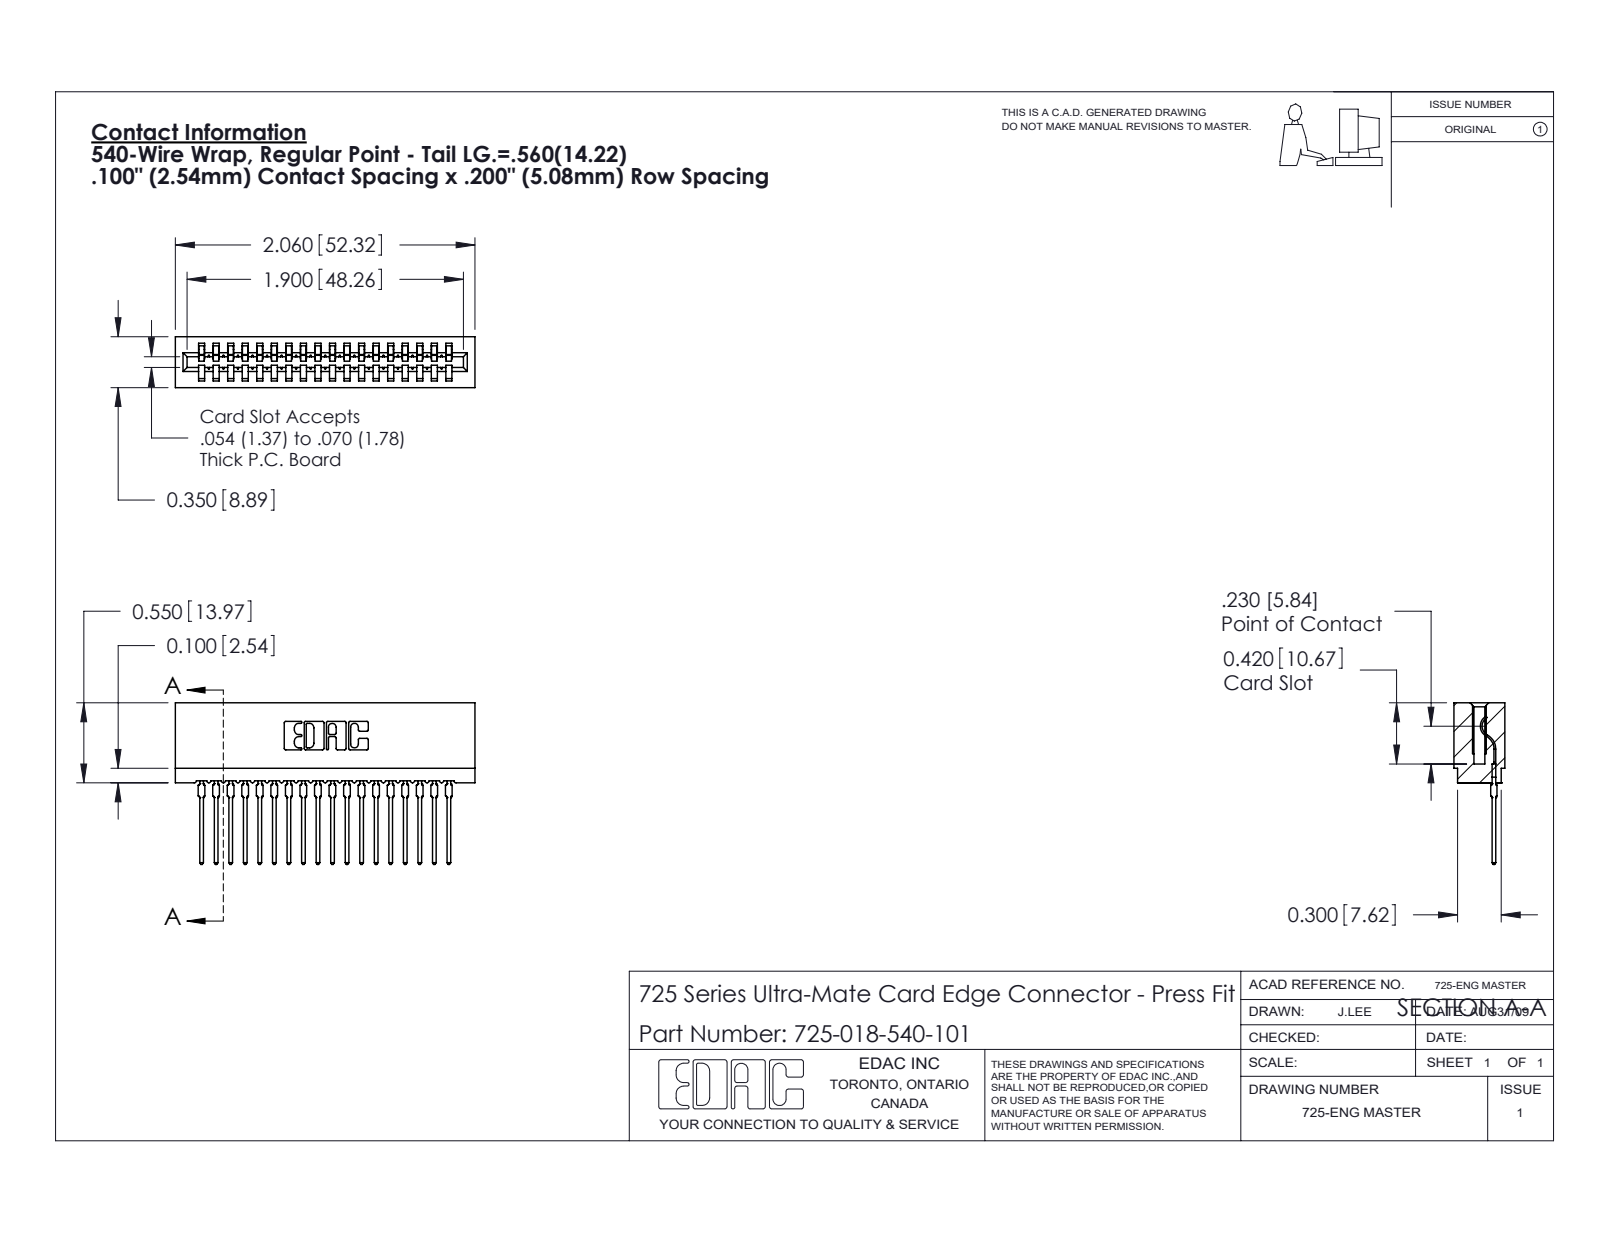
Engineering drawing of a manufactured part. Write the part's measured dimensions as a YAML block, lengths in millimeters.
part_name: "725 Part_Insulator Option - 01; 745-292-001_540; 725-018-540-101"
step_written_by: "SolidWorks 2020 (CONFIG_CONTROL_DESIGN)"
units: millimeters
bodies: {solids: 19, faces: 2111, planar: 1261, cylindrical: 382, other: 468}
overall_size: [52.3, 28.2, 8.9]
volume: 4150
surface_area: 7742
partial_cylinders:
  - {radius: 0.4, count: 36}
  - {radius: 0.5, count: 36}
  - {radius: 0.3, count: 22}
  - {radius: 0.2, count: 6}
  - {radius: 0.8, count: 6}
  - {radius: 0.1, count: 4}
  - {radius: 0.3, count: 4}
  - {radius: 0.7, count: 3}
face_to_face_distances: [2.5, 5.1, 7.6, 10.2, 12.7, 15.2, 17.8, 8.9, 20.3, 5.4]
